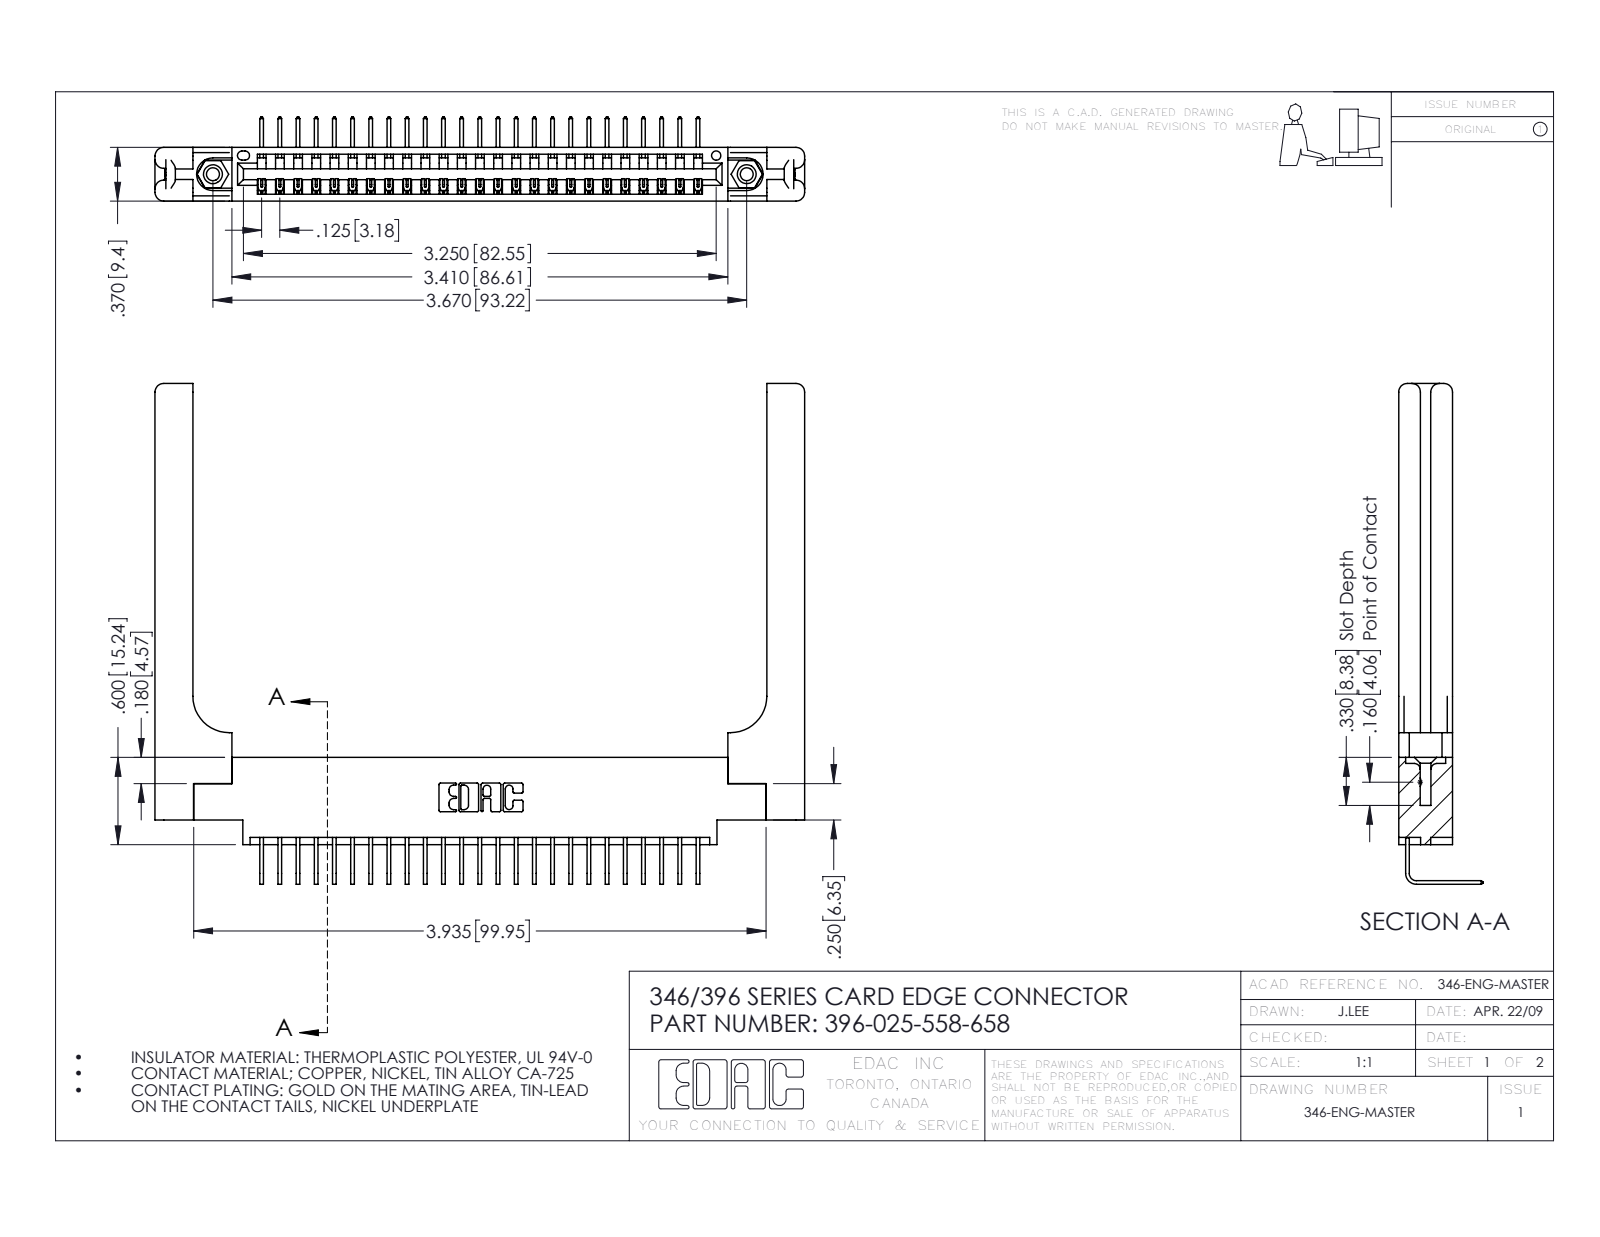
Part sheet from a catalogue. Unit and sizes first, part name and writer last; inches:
Units: inches
Overall size (bounding box): 4.466 × 3.443 × 0.58
Round holes (diameter × count): ⌀0.089 ×2, ⌀0.125 ×2, ⌀0.156 ×2, ⌀0.064 ×1
Round bosses / shafts (diameter × count): ⌀0.155 ×2
Partial cylindrical surfaces — rounded edges, fillets, slot ends (radius × count): R0.006 ×50, R0.01 ×22, R0.06 ×16, R0.007 ×6, R0.031 ×6, R0.026 ×3, R0.03 ×2, R0.031 ×2
Main face-to-face distances: 0.37, 0.322, 0.072, 0.048, 0.15, 0.148, 0.25, 0.025, 0.298, 0.077
Hole centre spacings: 0.246, 3.462, 3.67
Volume: 1.11 in³ · Surface area: 29.42 in²
Bodies: 30 solids, 1882 faces (1278 planar, 544 cylindrical, 60 other)
Part name (STEP PRODUCT): 396-025-558-658; 346 Part_0.170 Offset - 0.156 Dia-TH; 346-220-058_345-220-058; 345-250-001_345-250-001-102 (+1 more)
STEP written by: SolidWorks 2016 (CONFIG_CONTROL_DESIGN)
